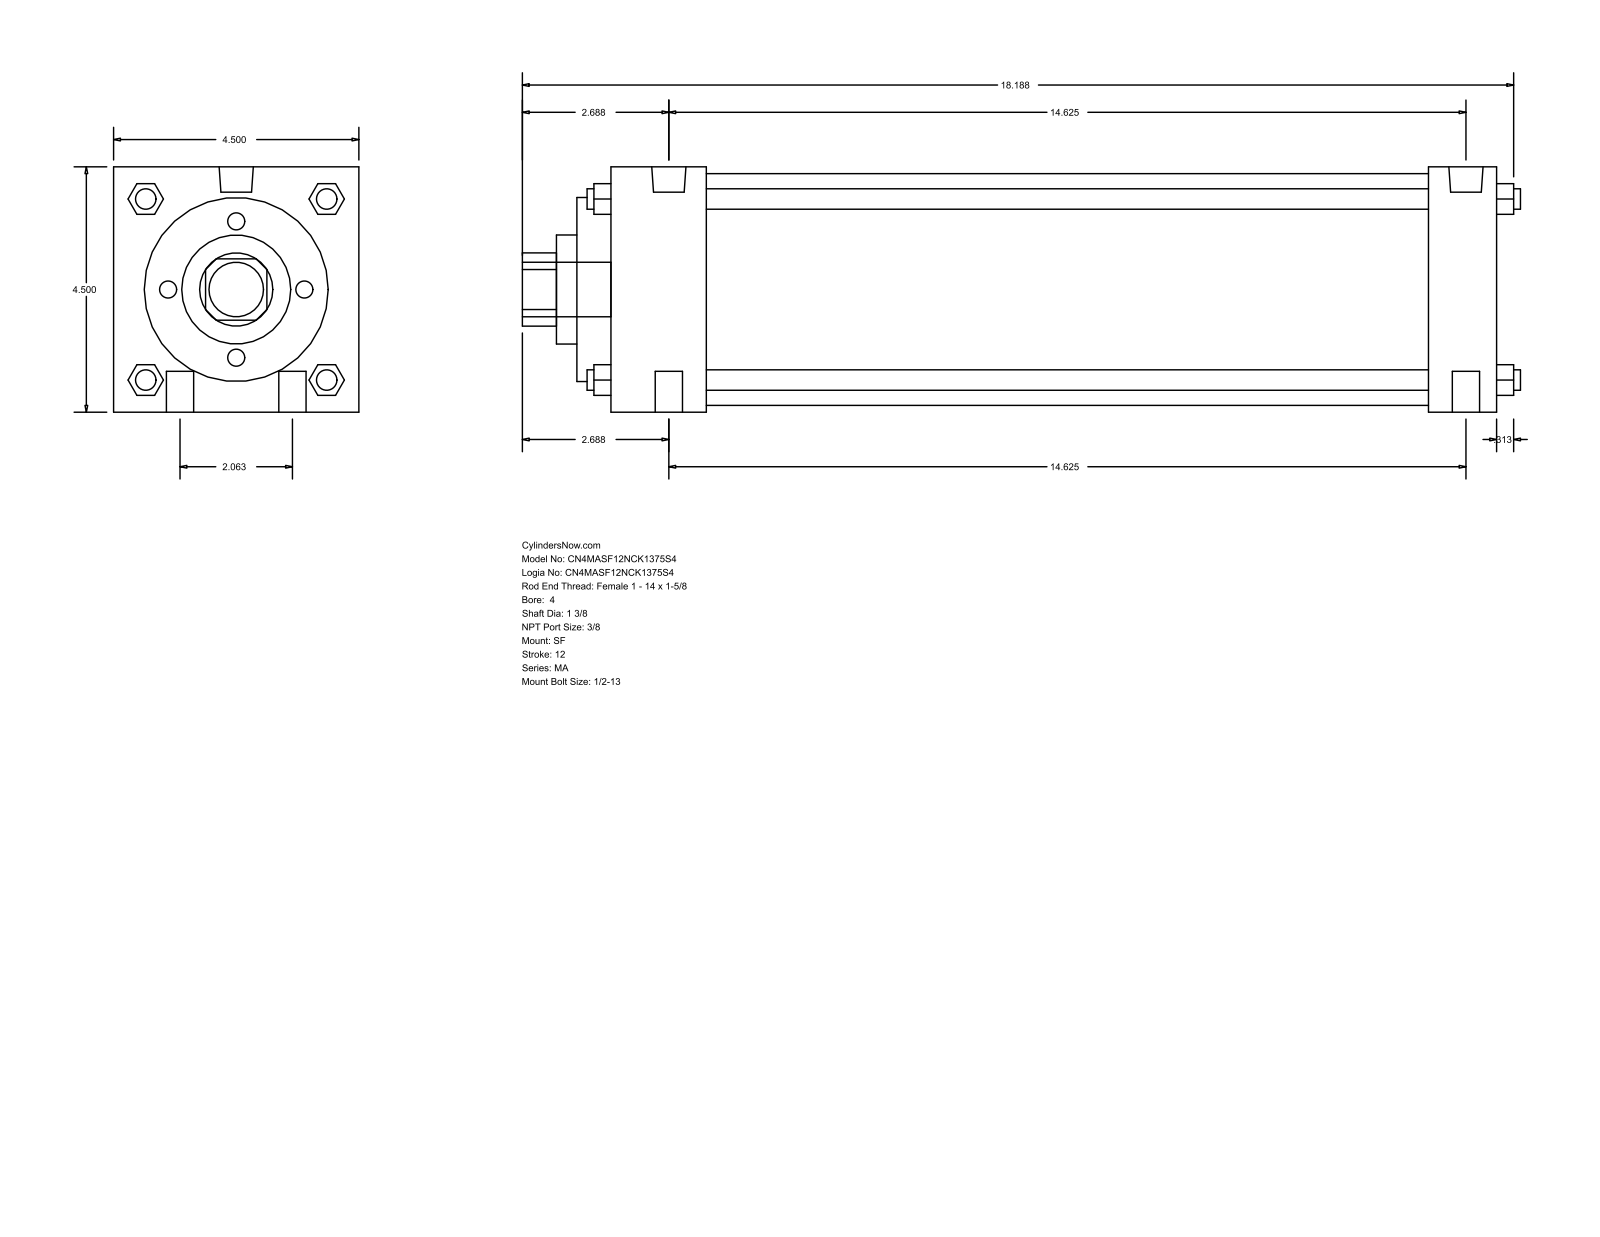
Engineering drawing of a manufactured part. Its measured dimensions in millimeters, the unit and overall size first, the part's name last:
Units: millimetres
Overall size (bounding box): 465.14 × 114.3 × 114.3
Round holes (diameter × count): ⌀34.92 ×1, ⌀50.8 ×1, ⌀85.72 ×1, ⌀107.95 ×1
Round bosses / shafts (diameter × count): ⌀12.7 ×4, ⌀9.53 ×4, ⌀15.93 ×2, ⌀11.11 ×2, ⌀25.4 ×1
Partial cylindrical surfaces — rounded edges, fillets, slot ends (radius × count): R17.06 ×1
Main face-to-face distances: 114.3, 412.75, 428.62, 15.87, 396.87, 381, 31.75, 60.32, 44.45, 336.55
Bodies: 0 solids, 126 faces (95 planar, 31 cylindrical, 0 other)
Part name (STEP PRODUCT): MA_SF__0400_1.375
STEP written by: GSSL Pune (CONFIG_CONTROL_DESIGN)
